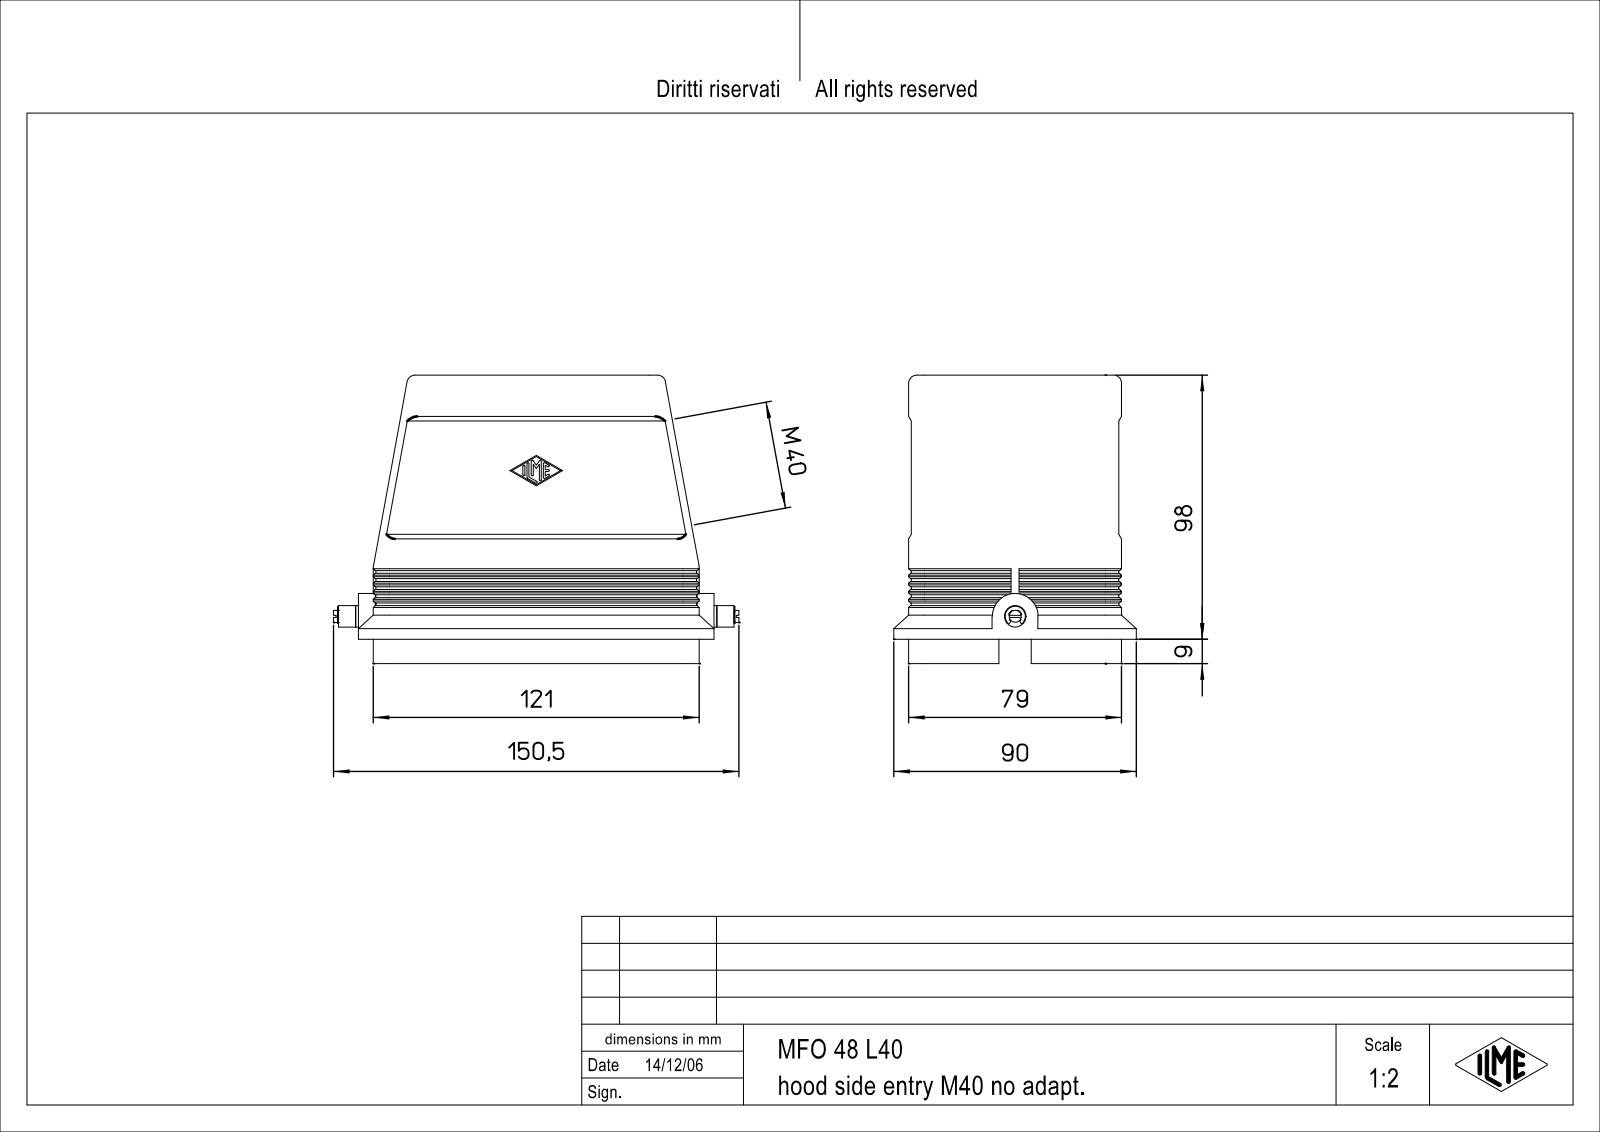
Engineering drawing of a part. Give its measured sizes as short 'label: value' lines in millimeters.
name: MFO_48_L32
written by: Creo Elements/Direct Modeling 17.0C 05-Feb-2011 (C) Parametric Technology GmbH (AUTOMOTIVE_DESIGN)
unit: mm
bodies: 1 solid, 565 faces (309 planar, 180 cylindrical, 76 other)
size: 150.5 × 107 × 90
volume: 236 465 mm³; area: 96 075 mm²
holes: 8× ⌀3.5, 6× ⌀2.46, 2× ⌀2.46, 1× ⌀6, 1× ⌀40
bosses: 1× ⌀8, 1× ⌀4.5, 1× ⌀3.5
rounds: 14× R0.38, 12× R2, 10× R6, 4× R0.5, 4× R3, 4× R5, 4× R11.5, 3× R0.95
face distances: 2.5, 74.5, 72, 3.5, 1, 75.5, 78, 13, 77, 8.5
hole spacings: 27, 35, 104, 107.45, 109.73, 8, 62, 104.31
